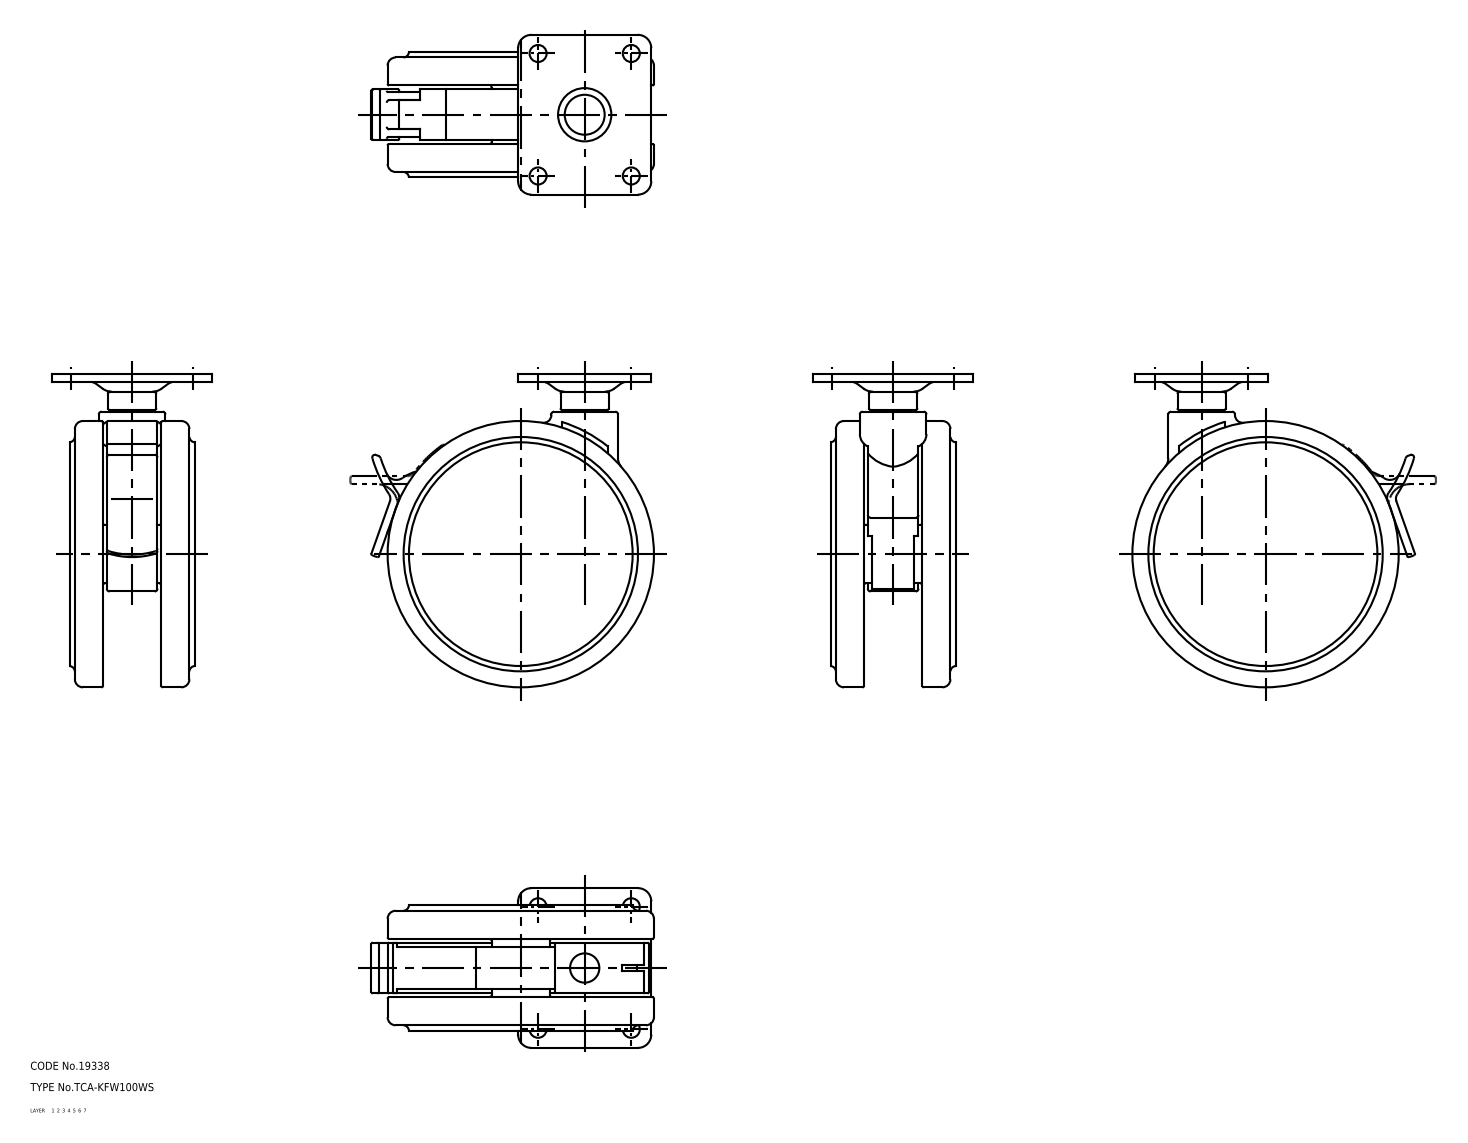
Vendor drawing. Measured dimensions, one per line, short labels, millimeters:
name: TCA_KFW100WS; main shaft; wheel; wheel_mr (+2 more)
written by: SolidWorks 2015 (AUTOMOTIVE_DESIGN)
unit: mm
bodies: 6 solids, 282 faces (64 planar, 110 cylindrical, 108 other)
size: 117.5 × 106.12 × 60
volume: 240 520 mm³; area: 67 613 mm²
holes: 4× ⌀6.4, 1× ⌀6, 1× ⌀72
bosses: 1× ⌀100, 1× ⌀25, 1× ⌀22, 1× ⌀18, 1× ⌀17, 1× ⌀15
rounds: 35× R0.5, 4× R5, 3× R3, 2× R1, 2× R47.5, 1× R1.5, 1× R2, 1× R4
face distances: 1.5, 12.5, 34.5, 7.5, 27, 39.5, 5, 3, 19, 14
hole spacings: 28.9, 35, 46, 57.8
